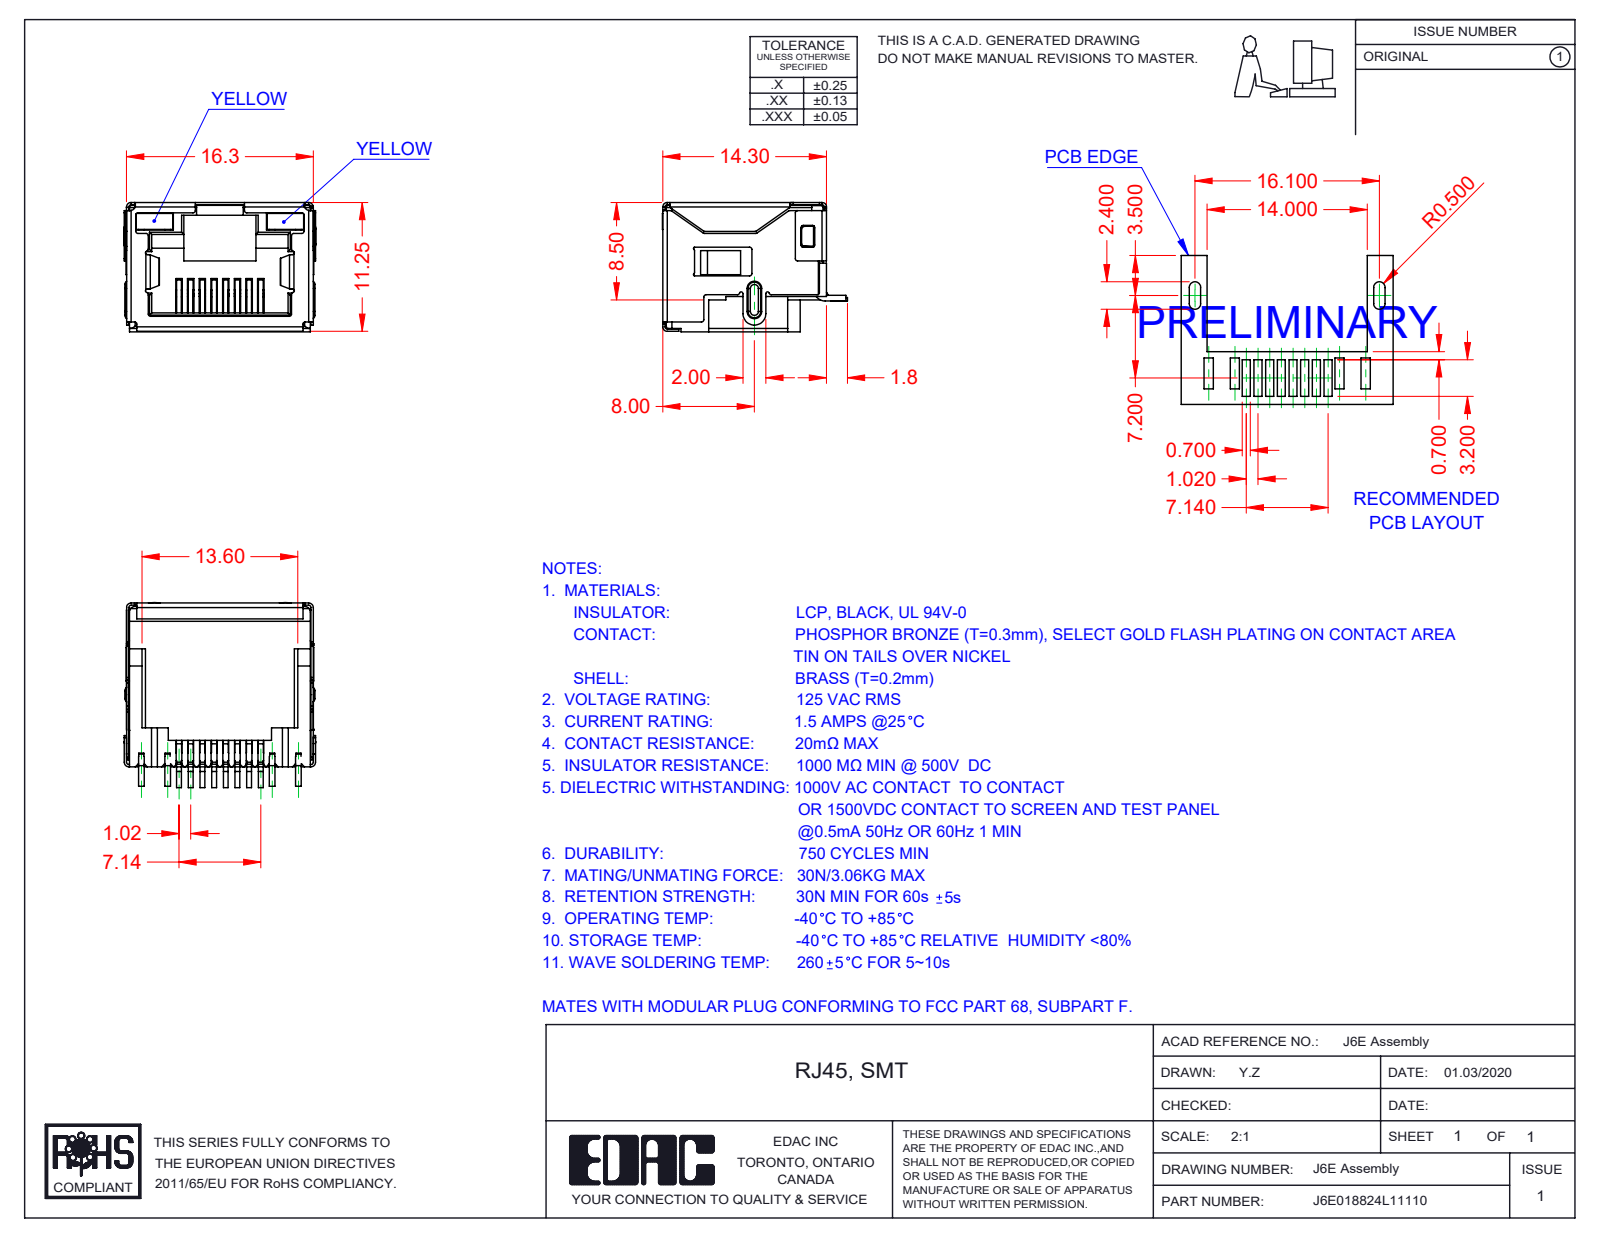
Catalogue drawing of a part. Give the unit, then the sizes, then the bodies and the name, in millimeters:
Units: millimetres
Overall size (bounding box): 16.75 × 16.15 × 11.3
Partial cylindrical surfaces — rounded edges, fillets, slot ends (radius × count): R0.2 ×82, R0.25 ×17, R0.4 ×13, R0.5 ×13, R0.1 ×10, R0.15 ×7, R0.3 ×4, R1 ×3
Main face-to-face distances: 11.05, 16.05, 16.1, 15.85, 11.1, 11.3, 2.4, 0.7, 9.85, 0.49
Volume: 1 109 mm³ · Surface area: 4 045 mm²
Bodies: 12 solids, 1496 faces (1099 planar, 347 cylindrical, 50 other)
Part name (STEP PRODUCT): 6E Insulator_LED; J6E018824L11110; 6E LED LH_1-Yellow; 6E LED RH_1-Yellow (+2 more)
STEP written by: SolidWorks 2016 (CONFIG_CONTROL_DESIGN)
